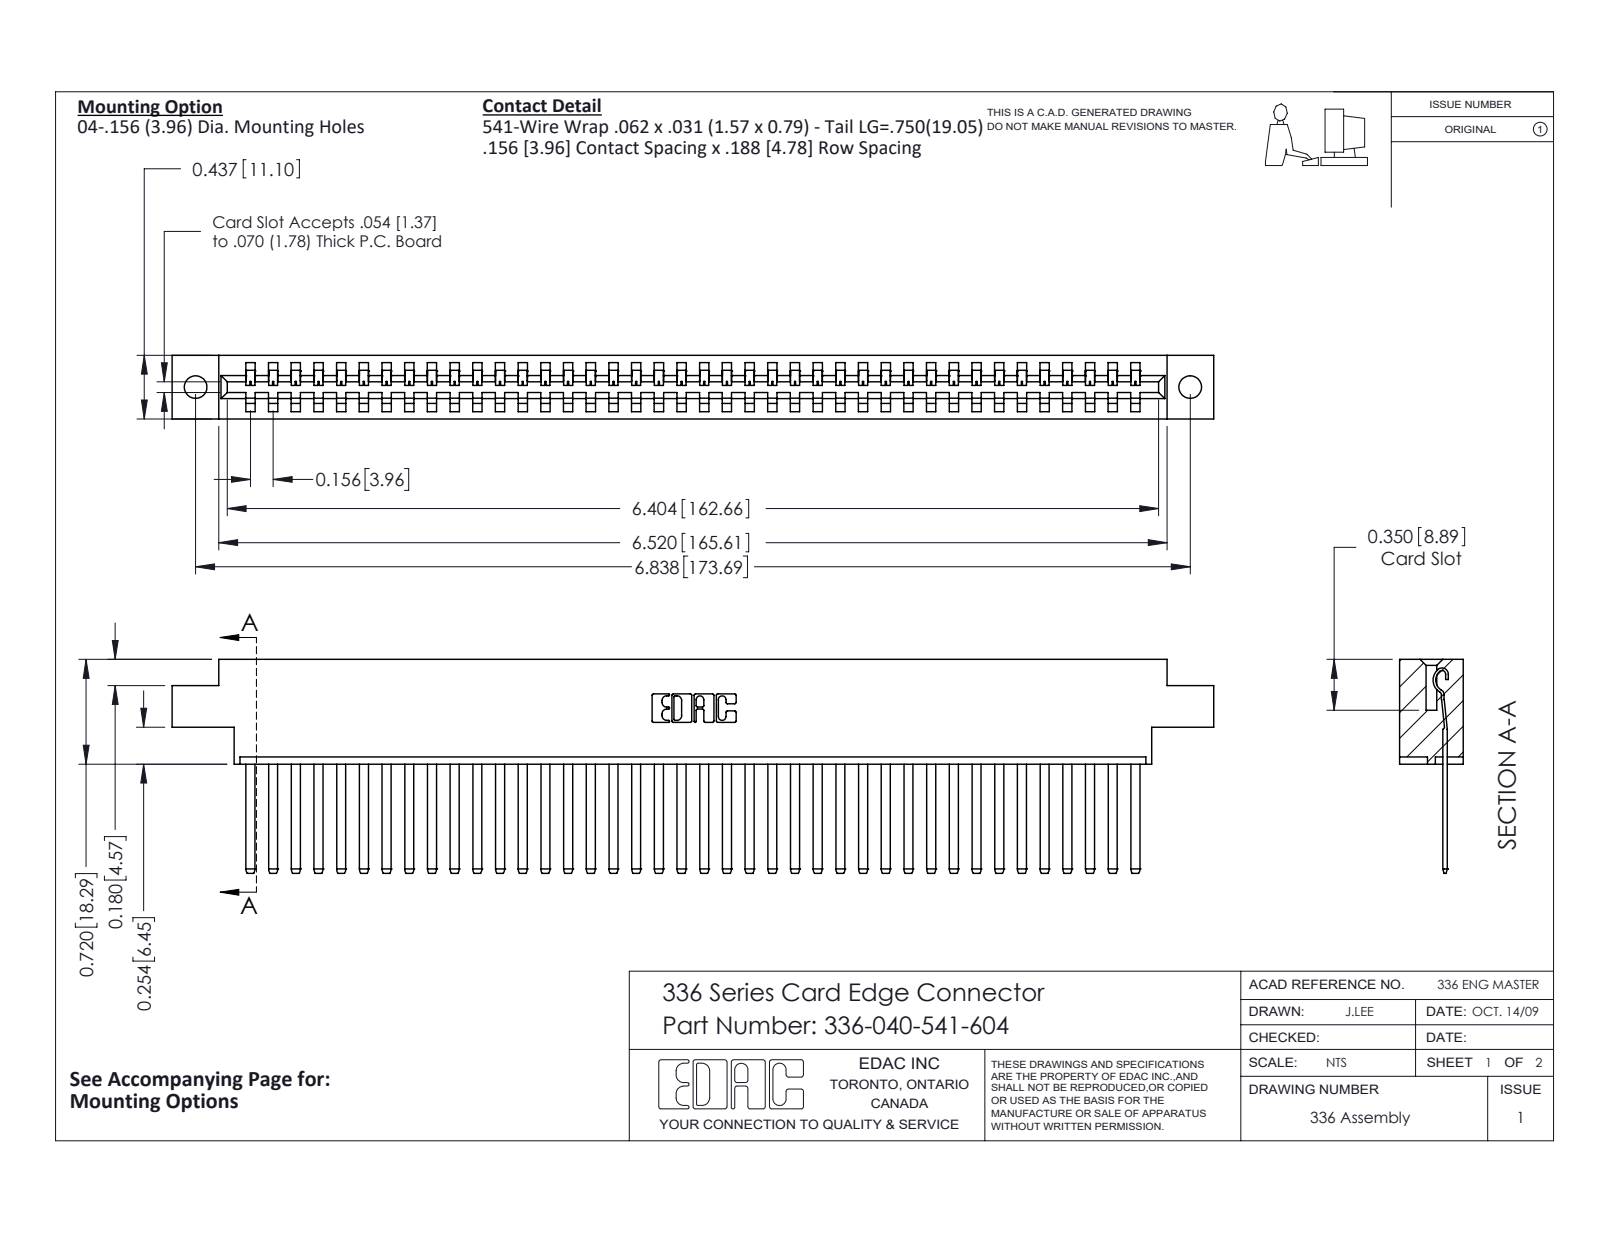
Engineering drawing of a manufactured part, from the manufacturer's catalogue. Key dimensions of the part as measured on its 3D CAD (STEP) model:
Part name (STEP PRODUCT): 336-290-001_336-290-541; 336 Part_Offset - .156 Dia - TH; 336-040-541-604
STEP written by: SolidWorks 2020 (CONFIG_CONTROL_DESIGN)
Units: inches
Bodies: 41 solids, 2118 faces (1434 planar, 684 cylindrical, 0 other)
Overall size (bounding box): 7.161 × 1.47 × 0.437
Volume: 1.608 in³ · Surface area: 44.24 in²
Round holes (diameter × count): ⌀0.156 ×2
Partial cylindrical surfaces — rounded edges, fillets, slot ends (radius × count): R0.004 ×80, R0.056 ×80, R0.01 ×22, R0.007 ×6, R0.031 ×6, R0.026 ×3, R0.022 ×2, R0.04 ×2
Main face-to-face distances: 0.437, 0.181, 0.328, 0.14, 0.297, 0.109, 0.031, 0.256, 0.05, 0.387
Hole centre spacings: 6.838
